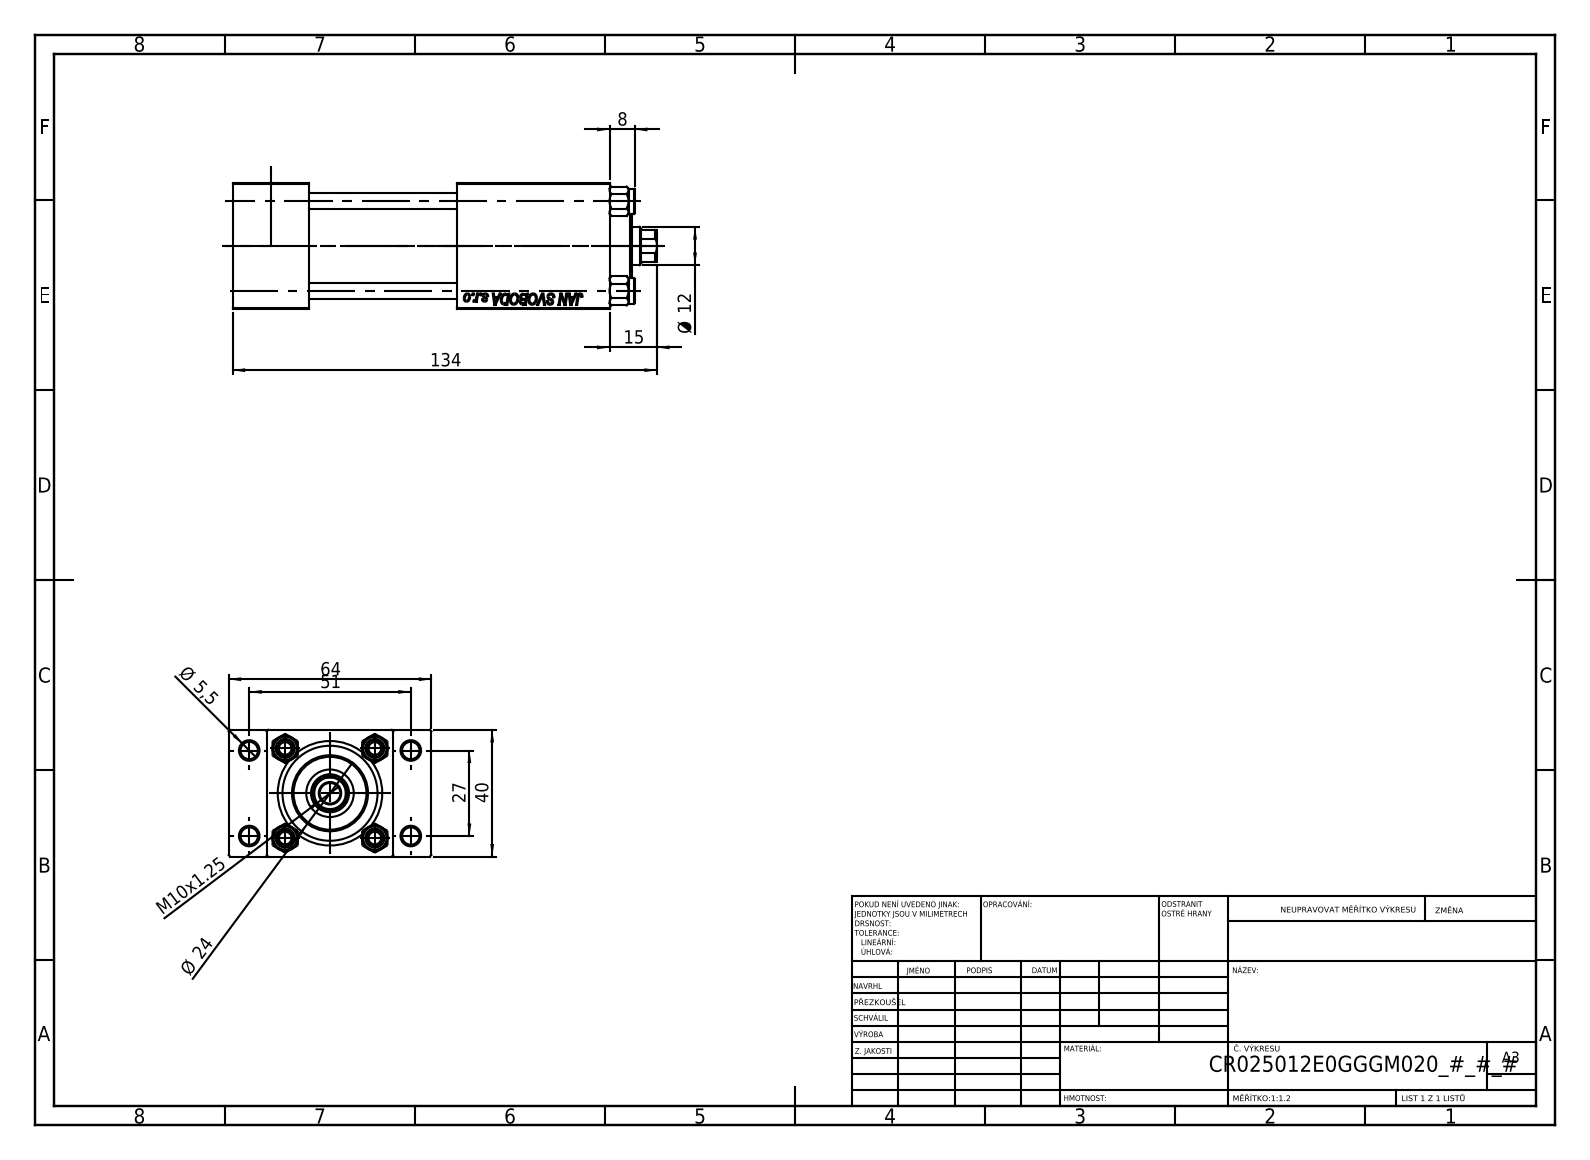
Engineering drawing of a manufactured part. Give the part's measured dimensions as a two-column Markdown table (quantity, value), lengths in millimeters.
| quantity | value |
| --- | --- |
| part name | V215CR_E_Body; V215_VC_A; V215CR_VCP_E; NUT_M5_E (+1 more) |
| STEP written by | SolidWorks 2019 (CONFIG_CONTROL_DESIGN) |
| units | millimeters |
| bodies | 11 solids, 1136 faces (497 planar, 87 cylindrical, 552 other) |
| overall size | 134 × 64 × 40 |
| volume | 163 915 mm³ |
| surface area | 62 105 mm² |
| round holes (diameter × count) | 5 × 4, 5.5 × 4, 20 × 3, 7 × 2, 13.16 × 2, 6.5 × 1, 12 × 1, 15 × 1, 25 × 1, 30 × 1 |
| round bosses / shafts (diameter × count) | 8 × 4, 31 × 1, 24 × 1 |
| partial cylindrical surfaces (radius × count) | 5.5 × 1 |
| main face-to-face distances | 40, 24, 12, 52, 119, 95, 90.3, 66.3, 28.7, 64 |
| hole center spacings | 11.37, 20.01, 28.3, 28.85, 29.89, 39.66, 48.34, 27 |
